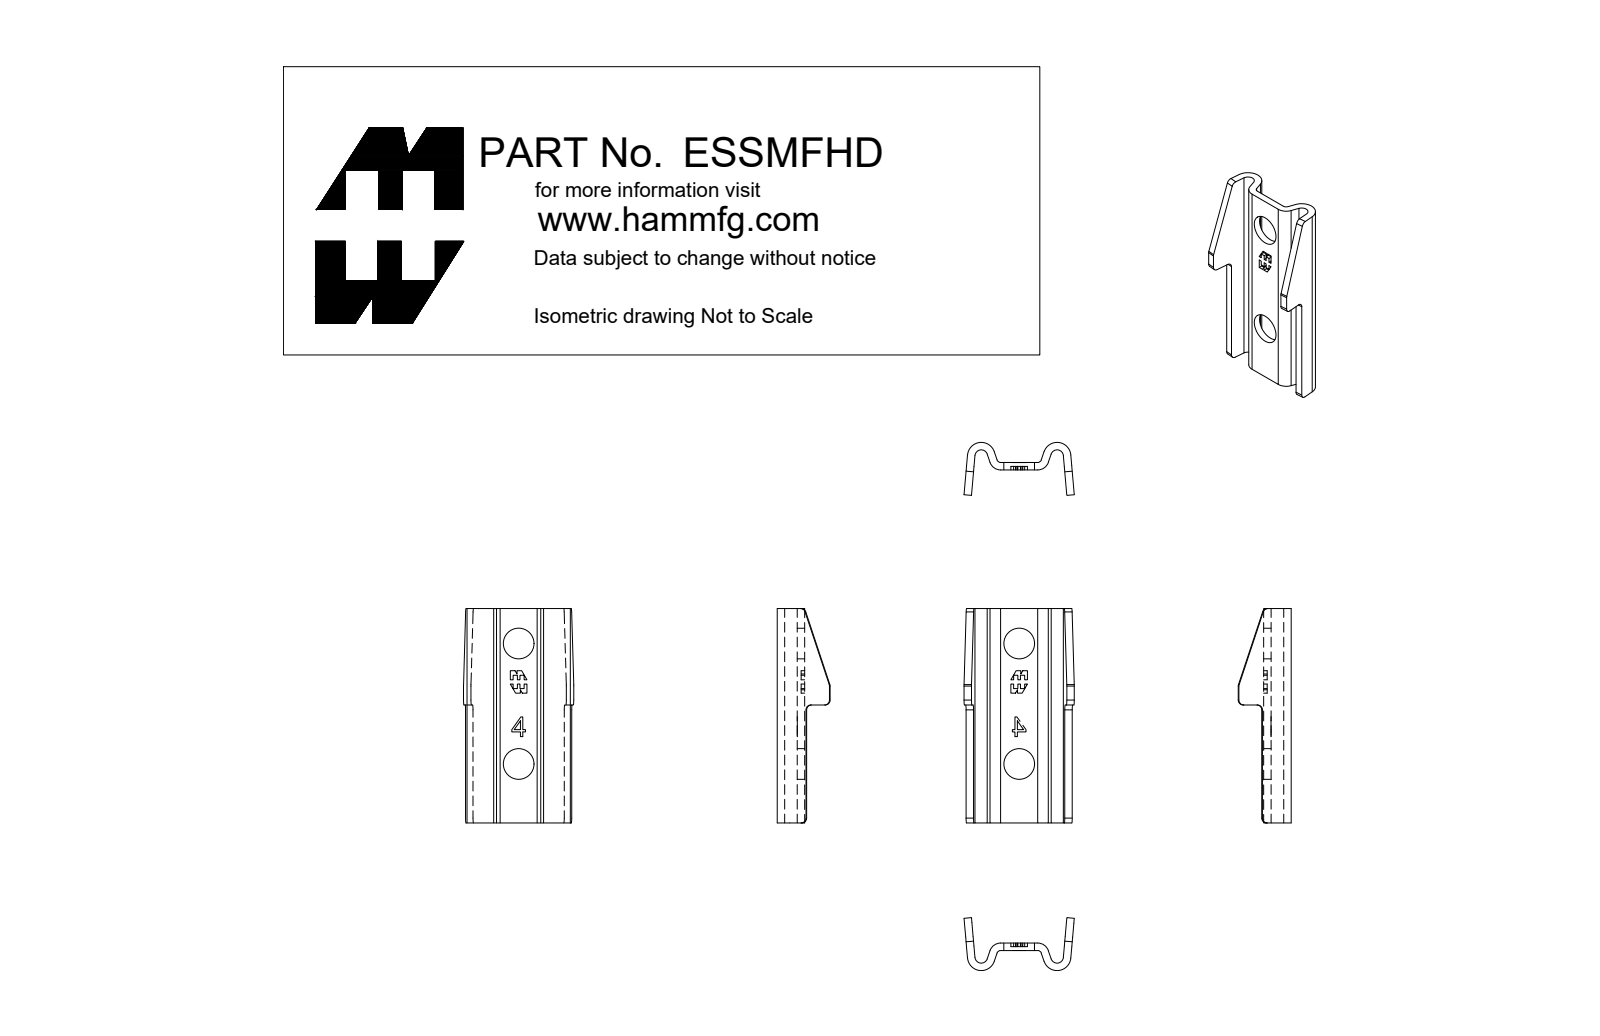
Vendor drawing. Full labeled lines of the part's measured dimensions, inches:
Part name (STEP PRODUCT): ESSMFHD
STEP written by: SolidWorks 2018 (AUTOMOTIVE_DESIGN)
Units: inches
Bodies: 1 solid, 90 faces (68 planar, 22 cylindrical, 0 other)
Overall size (bounding box): 2.726 × 1.402 × 0.673
Volume: 0.543 in³ · Surface area: 12.73 in²
Round holes (diameter × count): ⌀0.39 ×2
Partial cylindrical surfaces — rounded edges, fillets, slot ends (radius × count): R0.062 ×9, R0.048 ×2, R0.08 ×2, R0.143 ×2, R0.175 ×2, R0.063 ×1
Main face-to-face distances: 0.095, 0.095, 2.726, 0.299, 1.5, 1.226, 0.05, 0.045, 0.049, 0.094
Hole centre spacings: 1.531
